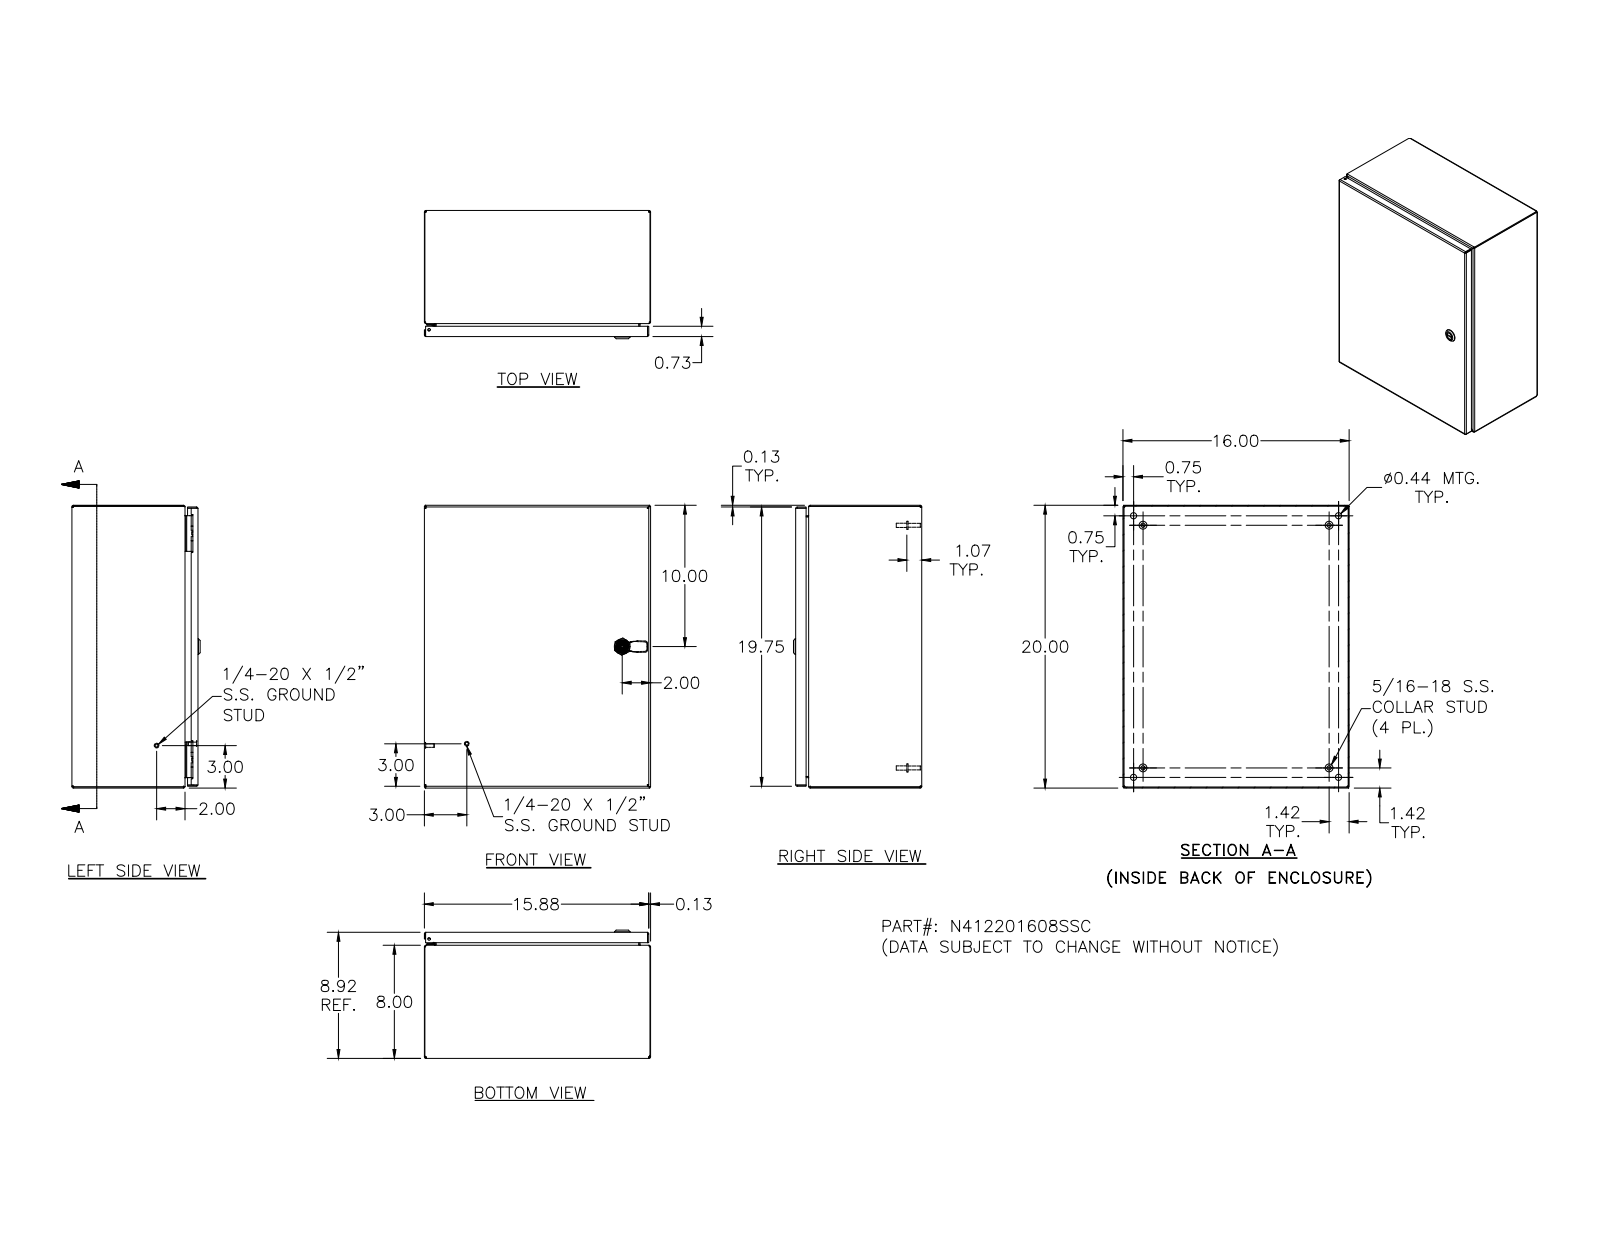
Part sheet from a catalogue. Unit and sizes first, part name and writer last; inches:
Units: inches
Overall size (bounding box): 20 × 16 × 9.075
Round holes (diameter × count): ⌀0.188 ×5, ⌀0.093 ×4, ⌀0.152 ×4, ⌀0.167 ×4, ⌀0.172 ×4, ⌀0.437 ×4, ⌀0.156 ×2, ⌀0.187 ×1, ⌀0.197 ×1, ⌀0.315 ×1, ⌀0.394 ×1, ⌀0.402 ×1
Round bosses / shafts (diameter × count): ⌀0.25 ×10, ⌀0.563 ×4, ⌀0.36 ×4, ⌀0.32 ×4, ⌀0.3 ×4, ⌀0.275 ×4, ⌀0.256 ×4, ⌀0.164 ×4
Partial cylindrical surfaces — rounded edges, fillets, slot ends (radius × count): R0.031 ×30, R0.05 ×26, R0.105 ×20, R0.016 ×18, R0.125 ×14, R0.02 ×9, R0.032 ×8, R0.07 ×8
Main face-to-face distances: 0.074, 8.843, 15.926, 8.769, 8.917, 19.926, 16, 15.852, 19.852, 20
Hole centre spacings: 16, 0.017, 0.66, 16.008, 0.019, 0.5, 0.648, 0.652
Volume: 101 in³ · Surface area: 2 748 in²
Bodies: 34 solids, 1384 faces (531 planar, 509 cylindrical, 344 other)
Part name (STEP PRODUCT): N412201608SSC; N412201608SSCBKP; 388151; N4122016SSCLID (+8 more)
STEP written by: Autodesk Inventor 2011 (AUTOMOTIVE_DESIGN)
